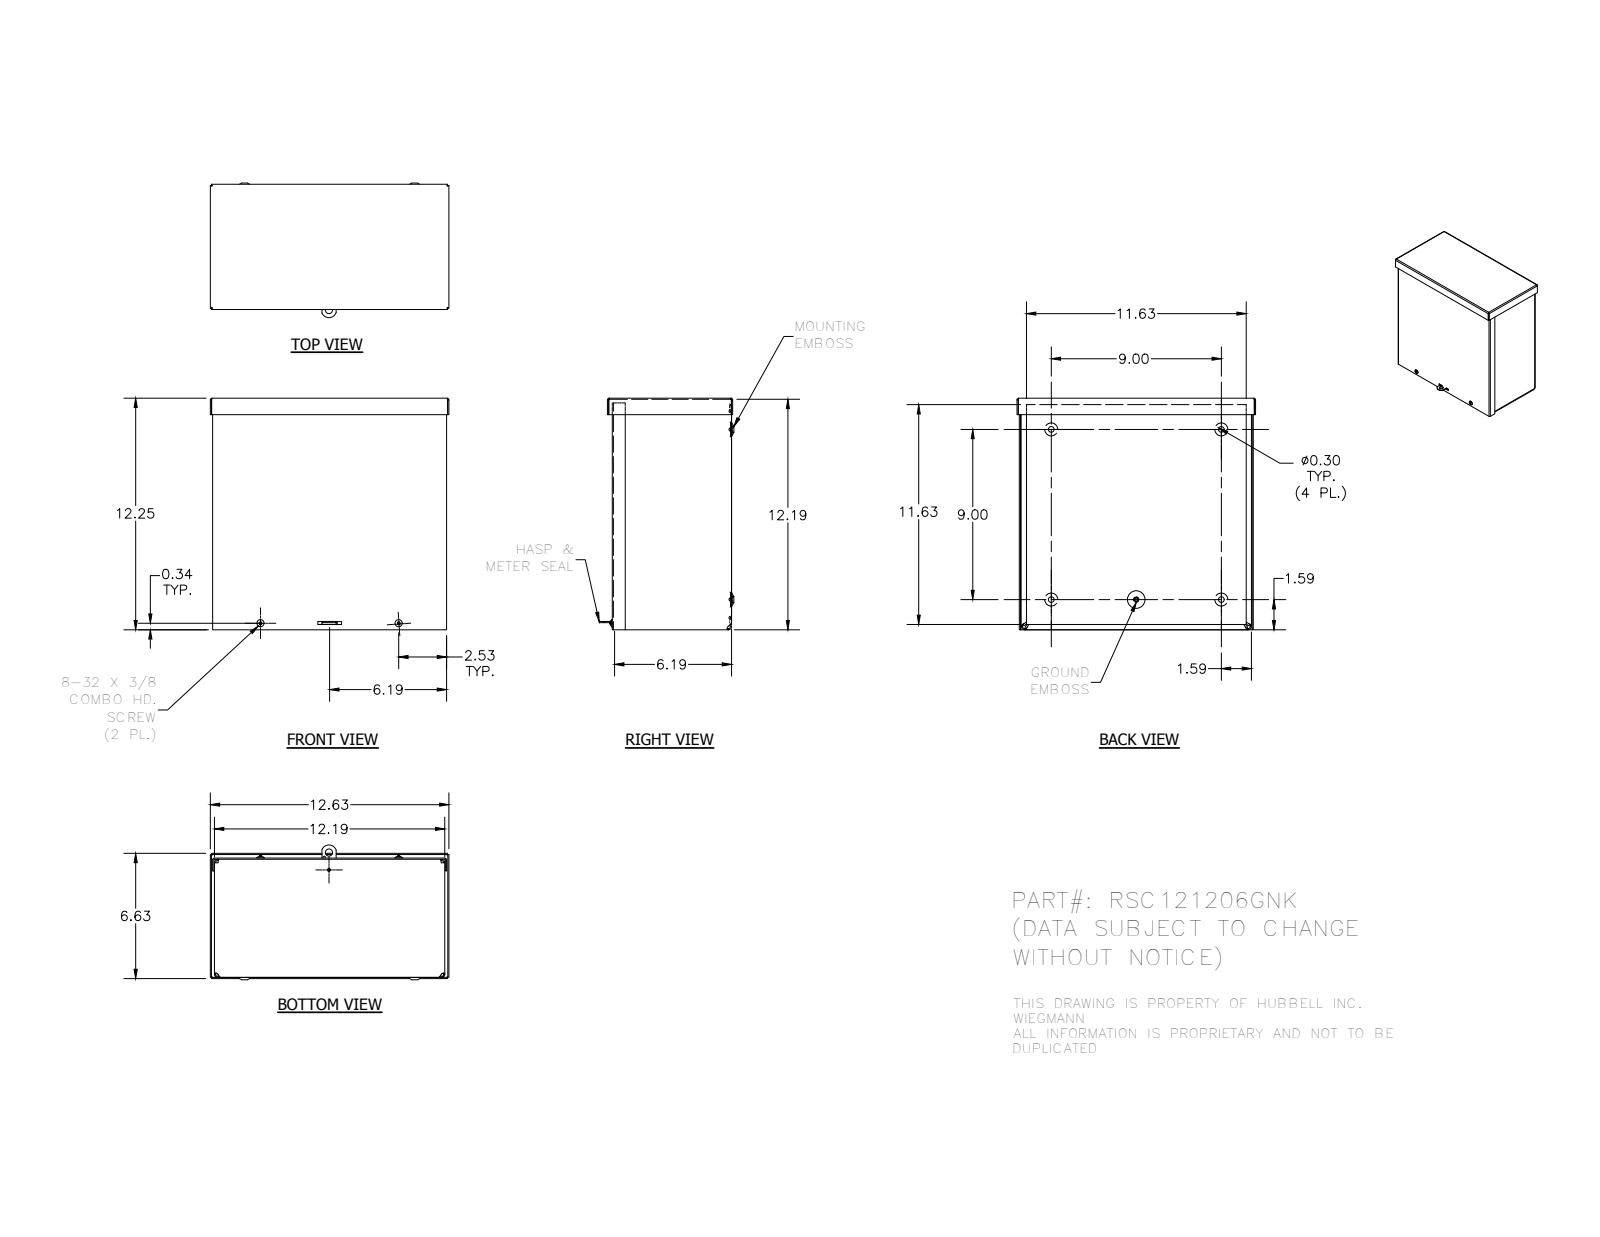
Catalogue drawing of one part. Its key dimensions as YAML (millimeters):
part_name: "RSC121206GNK_WRAP; RSC1212GNK_LID; RSC1206GNK_CAP; 3183 (+3 more)"
step_written_by: "Autodesk Inventor 2014 (AUTOMOTIVE_DESIGN)"
units: millimeters
bodies: {solids: 7, faces: 377, planar: 163, cylindrical: 78, other: 136}
overall_size: [320.68, 311.16, 180.97]
volume: 792360
surface_area: 1017000
round_holes:
  - {diameter: 7.62, count: 4}
  - {diameter: 7.95, count: 4}
  - {diameter: 3.17, count: 2}
  - {diameter: 3.76, count: 2}
  - {diameter: 3.96, count: 1}
  - {diameter: 4.19, count: 1}
  - {diameter: 9.52, count: 1}
round_bosses_or_shafts:
  - {diameter: 9.75, count: 2}
  - {diameter: 4.17, count: 2}
  - {diameter: 5.8, count: 1}
partial_cylinders:
  - {radius: 0.79, count: 8}
  - {radius: 2.37, count: 8}
  - {radius: 3.17, count: 8}
  - {radius: 4.75, count: 8}
  - {radius: 1.4, count: 4}
  - {radius: 1.57, count: 4}
  - {radius: 2.38, count: 4}
  - {radius: 2.97, count: 4}
face_to_face_distances: [1.58, 307.99, 1.57, 158.73, 157.15, 309.57, 1.59, 160.32, 158.74, 3.15]
hole_center_spacings: [228.6, 34.43, 114.3, 185.75, 255.57, 256.45, 261.26, 287.33]
